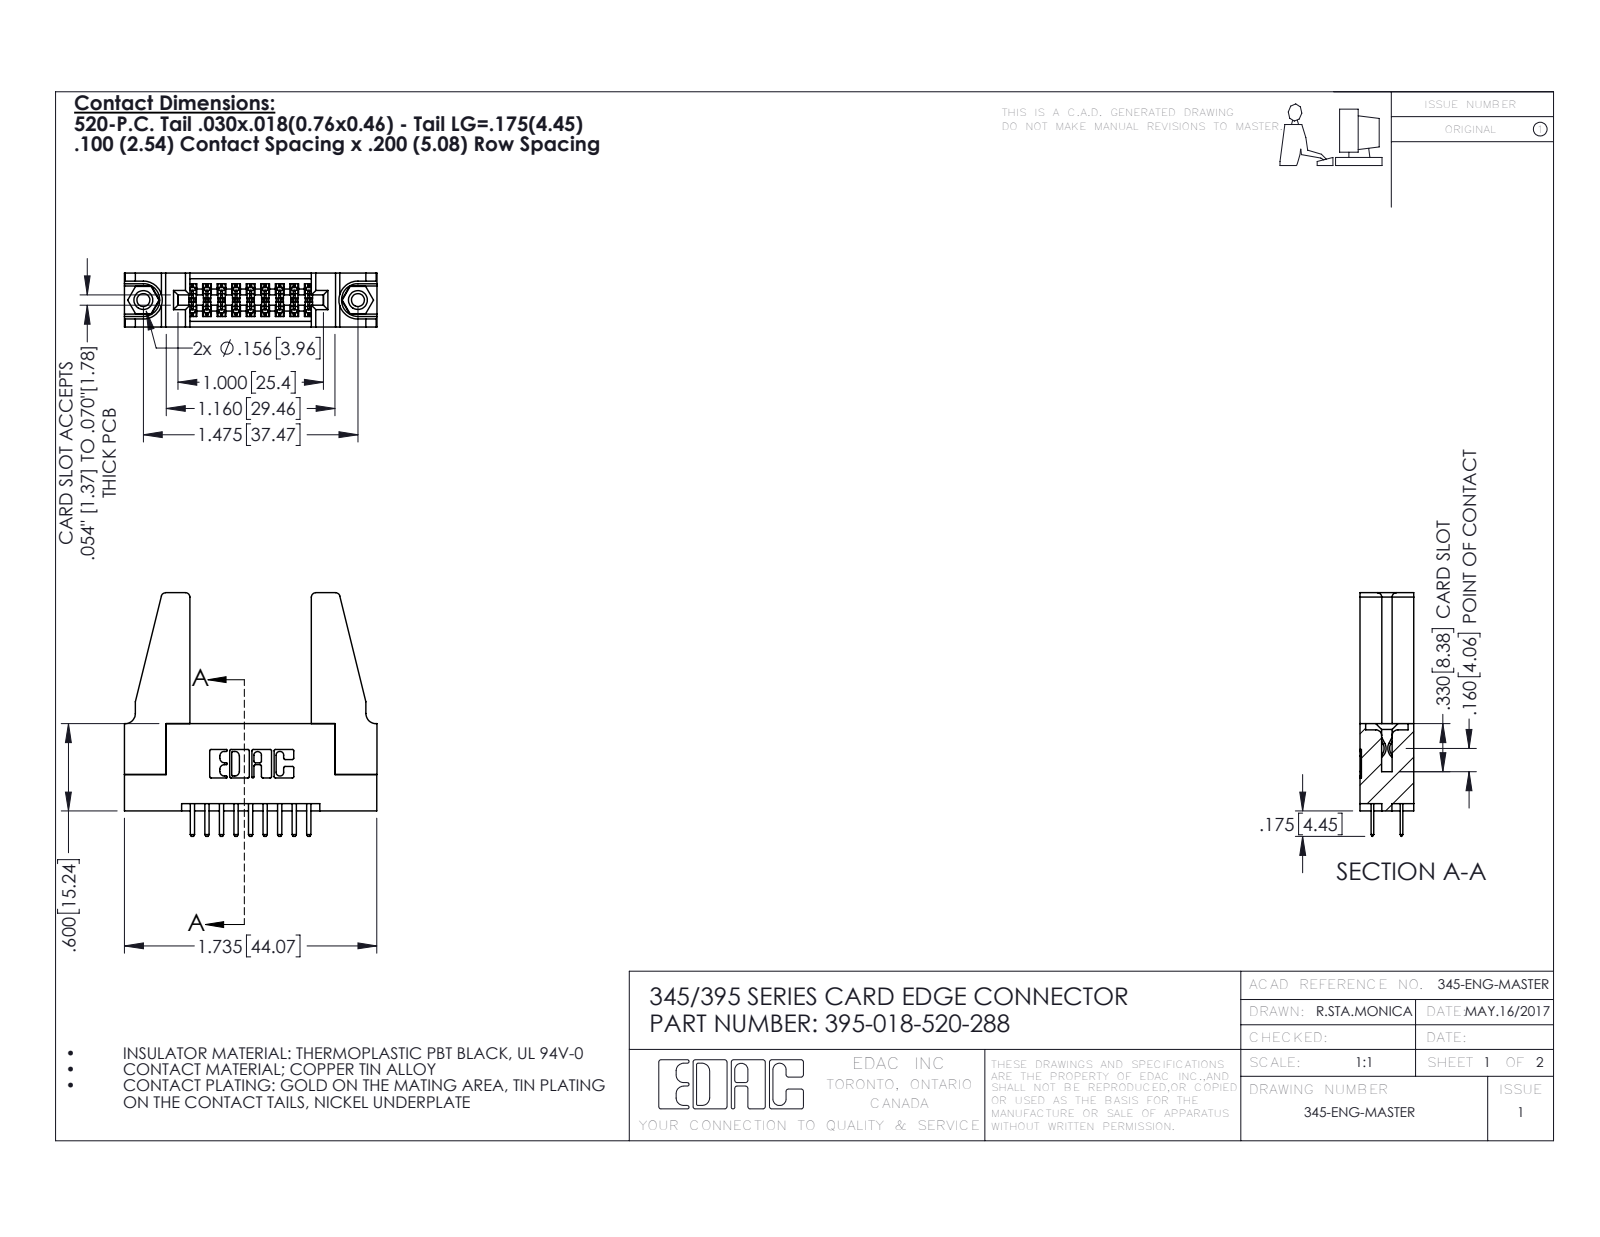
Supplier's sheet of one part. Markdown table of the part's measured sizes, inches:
| quantity | value |
| --- | --- |
| part name | 395-018-520-288; 345-220-078_345-220-088; 345-292-001_345-293-120; 345 Part_Flush Mounting Lugs - 0.156 Dia-TH (+1 more) |
| STEP written by | SolidWorks 2016 (CONFIG_CONTROL_DESIGN) |
| units | inches |
| bodies | 23 solids, 1222 faces (782 planar, 424 cylindrical, 16 other) |
| overall size | 1.736 × 1.675 × 0.37 |
| volume | 0.441 in³ |
| surface area | 12.92 in² |
| round holes (diameter × count) | 0.089 × 2, 0.125 × 2, 0.156 × 2, 0.064 × 1 |
| round bosses / shafts (diameter × count) | 0.155 × 2 |
| partial cylindrical surfaces (radius × count) | 0.006 × 27, 0.01 × 22, 0.01 × 22, 0.03 × 8, 0.007 × 6, 0.031 × 6, 0.026 × 3, 0.014 × 2 |
| main face-to-face distances | 0.37, 0.072, 0.298, 0.2, 0.225, 0.098, 0.272, 0.025, 0.25, 0.148 |
| hole center spacings | 0.27, 1.244, 1.475 |
